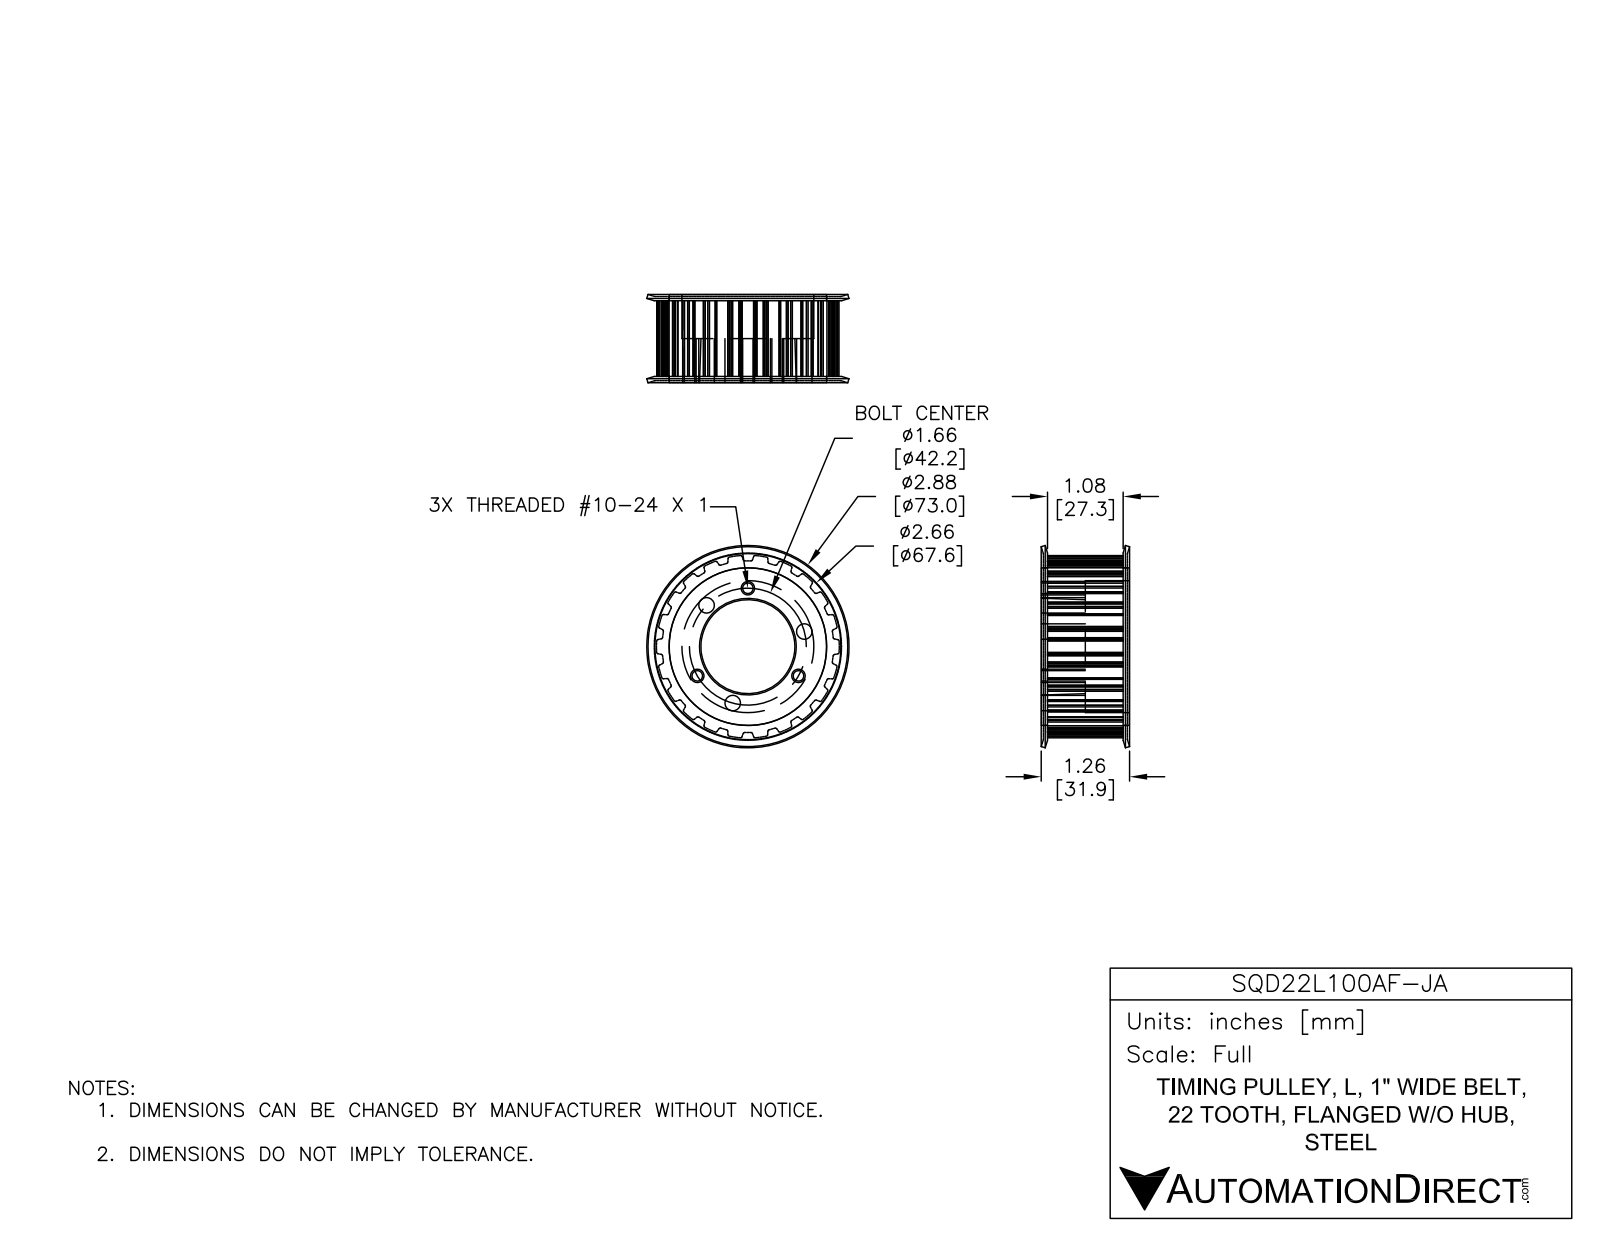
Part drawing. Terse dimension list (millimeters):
name: SQD22L100AF-JA
written by: SolidWorks 2018 (AUTOMOTIVE_DESIGN)
unit: mm
bodies: 1 solid, 241 faces (78 planar, 149 cylindrical, 14 other)
size: 73 × 73 × 31.9
volume: 60 290 mm³; area: 22 660 mm²
holes: 3× ⌀3.8, 3× ⌀5.6, 1× ⌀47.6, 1× ⌀56.9
bosses: 1× ⌀56.8
rounds: 88× R0.5, 1× R33
face distances: 0.7, 31, 30.4, 15.2, 15.2, 15.9, 15.9, 31.8, 13.6, 29.5
hole spacings: 21.1, 36.5, 16.1, 25.7, 41.8, 16.2, 21.1, 21.1
